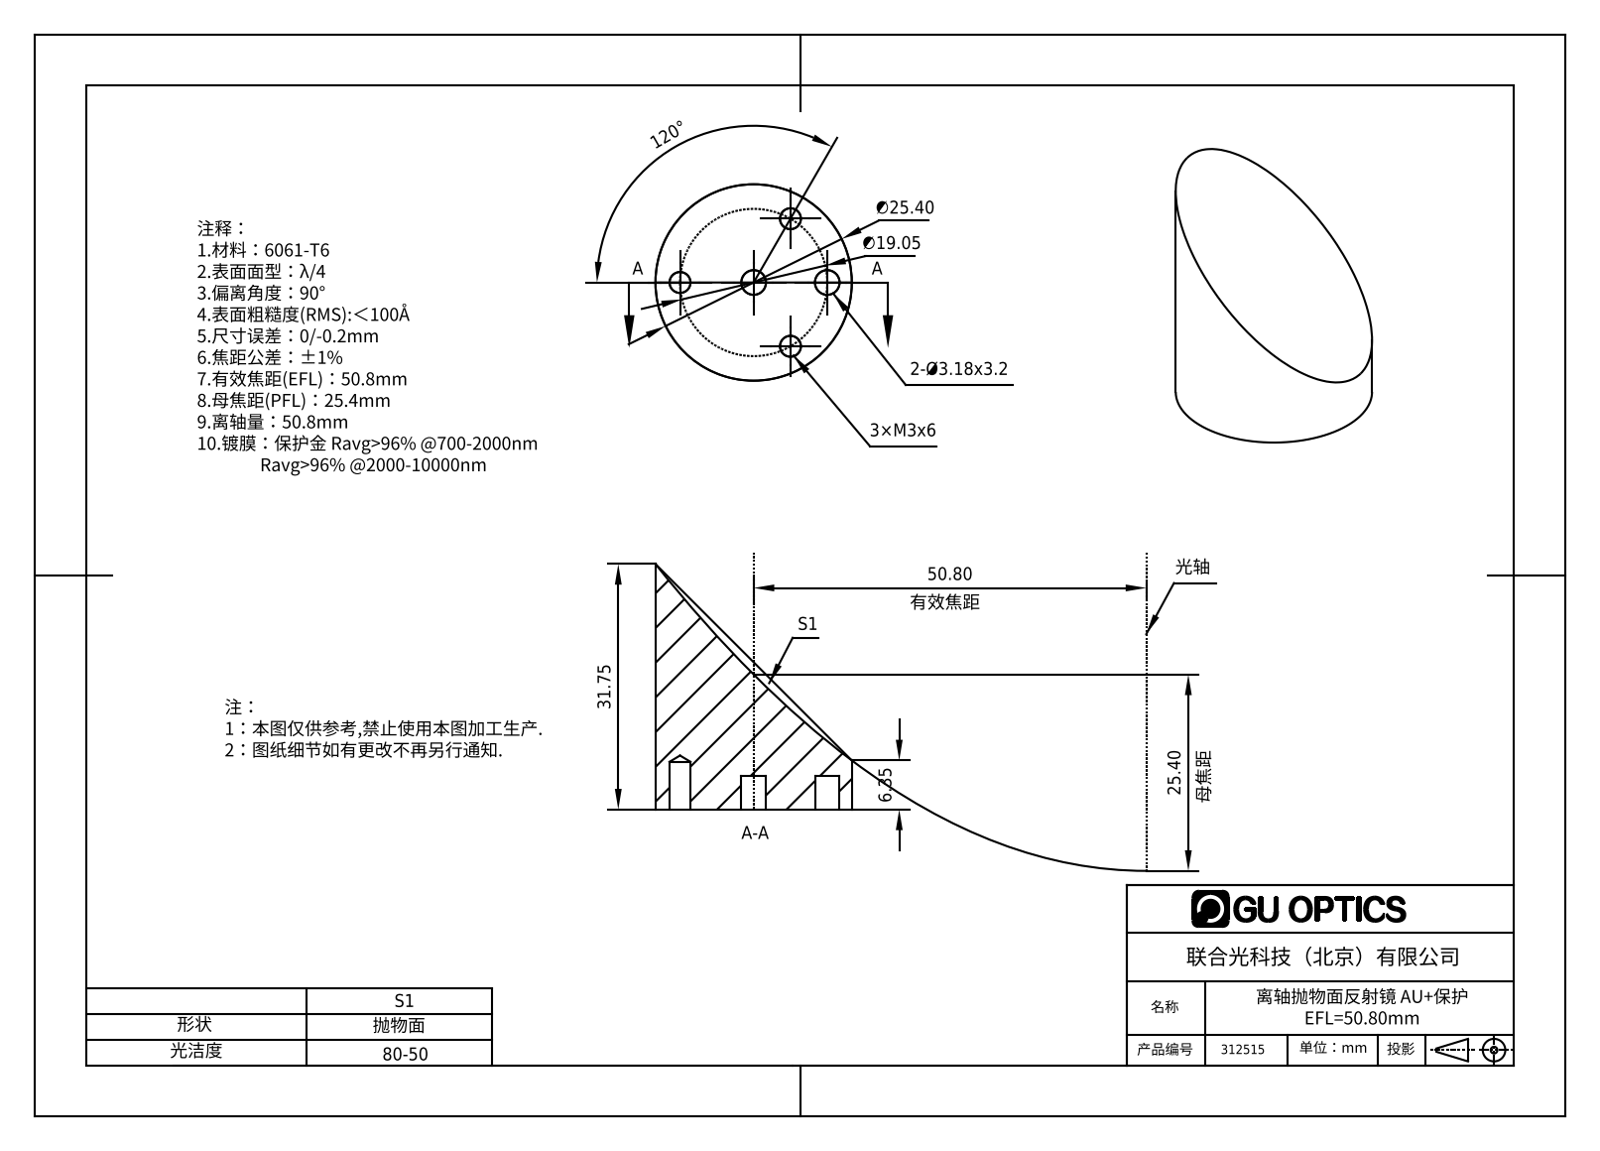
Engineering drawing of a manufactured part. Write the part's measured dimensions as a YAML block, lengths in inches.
part_name: "Ø25_36587"
step_written_by: "SolidWorks 2018 (CONFIG_CONTROL_DESIGN)"
units: inches
bodies: {solids: 1, faces: 23, planar: 3, cylindrical: 12, other: 8}
overall_size: [1.25, 1, 1]
volume: 0.554
surface_area: 4.641
round_holes:
  - {diameter: 0.107, count: 3}
  - {diameter: 0.126, count: 2}
round_bosses_or_shafts:
  - {diameter: 1, count: 1}
face_to_face_distances: [0.17]
hole_center_spacings: [0.375, 0.65, 0.375, 0.75]
